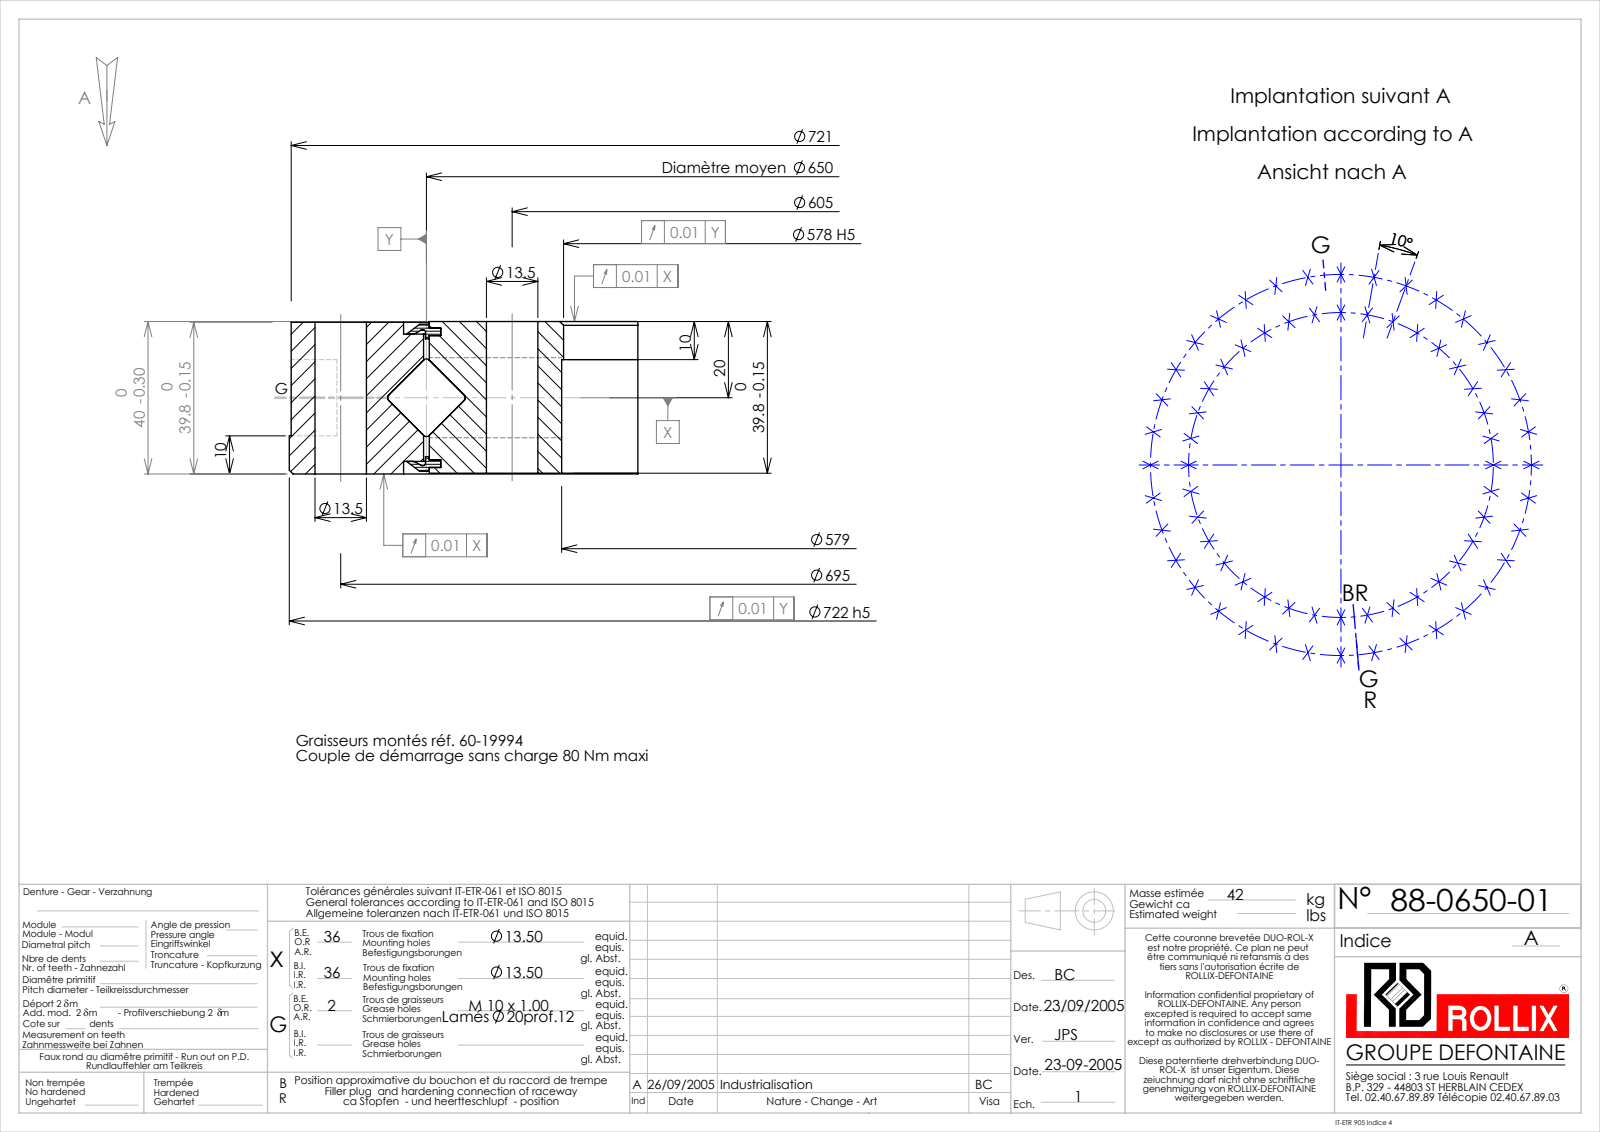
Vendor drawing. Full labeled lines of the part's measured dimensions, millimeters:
Part name (STEP PRODUCT): 88-0650-01
STEP written by: SolidWorks 2016 (CONFIG_CONTROL_DESIGN)
Units: millimetres
Bodies: 7 solids, 303 faces (46 planar, 202 cylindrical, 55 other)
Overall size (bounding box): 722 × 722 × 40
Volume: 4 832 000 mm³ · Surface area: 874 325 mm²
Round holes (diameter × count): ⌀13.5 ×72, ⌀9 ×2, ⌀20 ×2, ⌀578 ×1, ⌀579 ×1, ⌀642.5 ×1, ⌀648.5 ×1, ⌀651.5 ×1, ⌀662 ×1
Round bosses / shafts (diameter × count): ⌀10 ×2, ⌀722 ×1, ⌀721 ×1, ⌀650.5 ×1, ⌀15 ×1
Main face-to-face distances: 39.8, 39.6, 40, 3.1, 36.9, 2.9, 36.7, 3.5, 36.5, 3.3
Hole centre spacings: 293.72, 347.5, 532.4, 569.31, 629.88, 684.44, 60.57, 692.35
